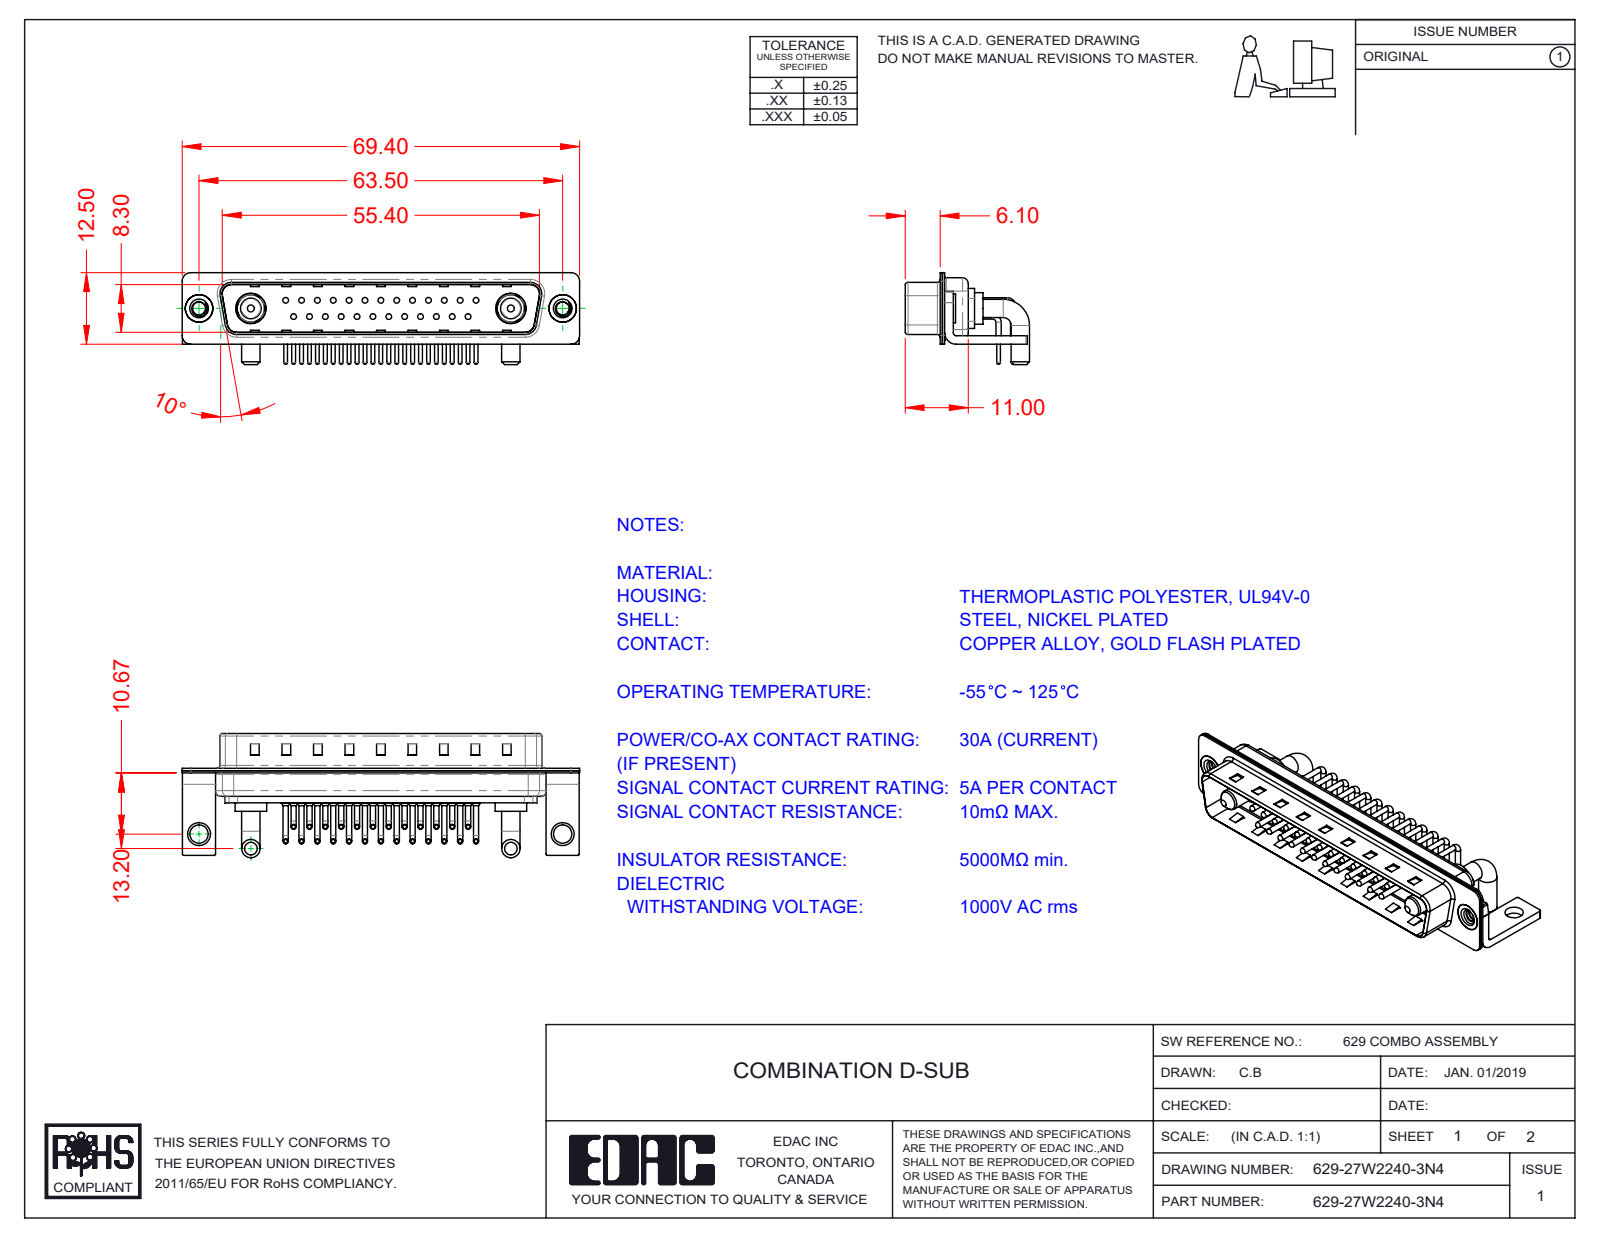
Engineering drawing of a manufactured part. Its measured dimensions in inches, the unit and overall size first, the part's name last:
Units: inches
Overall size (bounding box): 2.732 × 0.854 × 0.632
Round holes (diameter × count): ⌀0.03 ×25, ⌀0.063 ×25, ⌀0.079 ×25, ⌀0.089 ×2, ⌀0.126 ×2, ⌀0.157 ×2, ⌀0.189 ×2, ⌀0.191 ×2, ⌀0.209 ×2
Round bosses / shafts (diameter × count): ⌀0.035 ×50, ⌀0.059 ×25, ⌀0.039 ×25, ⌀0.026 ×25, ⌀0.126 ×4, ⌀0.217 ×2, ⌀0.205 ×2, ⌀0.197 ×2
Partial cylindrical surfaces — rounded edges, fillets, slot ends (radius × count): R0.04 ×25, R0.01 ×16, R0.059 ×16, R0.079 ×13, R0.02 ×9, R0.063 ×8, R0.024 ×4, R0.026 ×4
Main face-to-face distances: 0.016, 0.031, 0.374, 0.358, 0.343, 0.059, 0.39, 0.03, 0.22, 0.047
Hole centre spacings: 0.124, 0.109, 0.218, 0.327, 0.198, 0.294, 0.436, 0.198
Volume: 0.278 in³ · Surface area: 16.62 in²
Bodies: 36 solids, 3288 faces (1843 planar, 1101 cylindrical, 344 other)
Part name (STEP PRODUCT): Power Pin_30A RA; 629Combo Stabilizer Bracket; 629Combo Shell Front_37 Contacts; 629Combo Contact Row 1 (+5 more)
STEP written by: SolidWorks 2020 (CONFIG_CONTROL_DESIGN)
